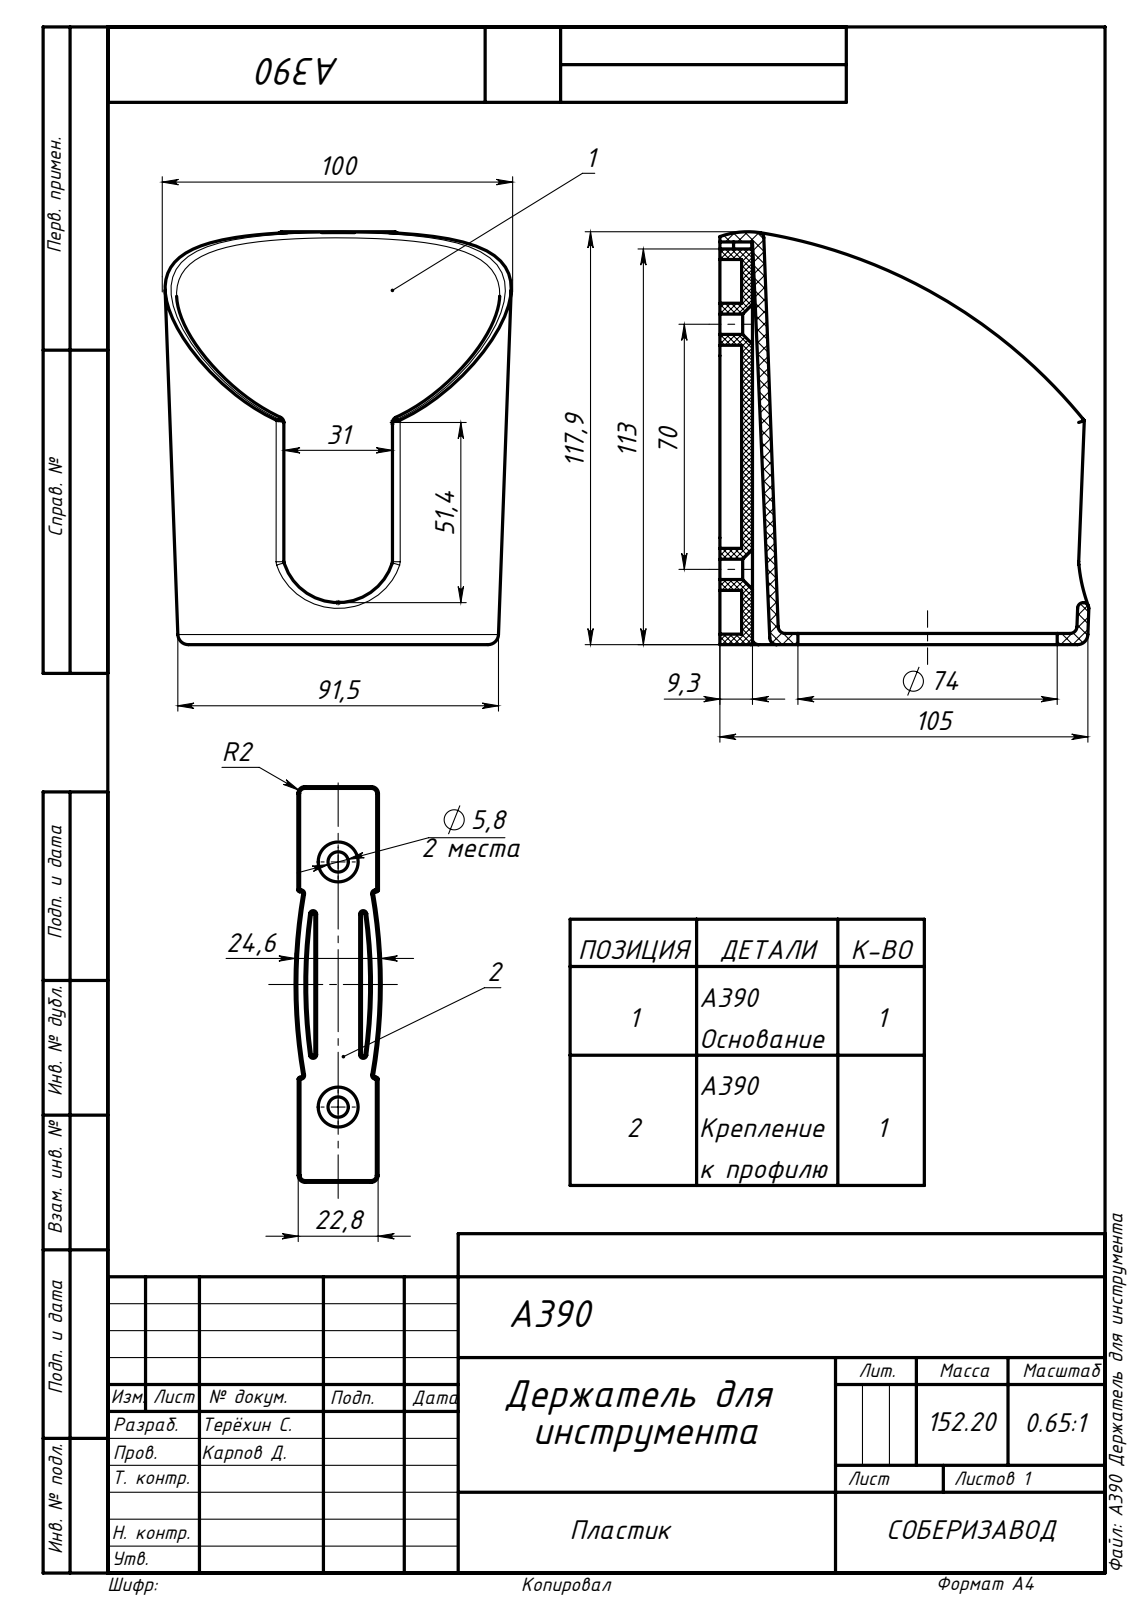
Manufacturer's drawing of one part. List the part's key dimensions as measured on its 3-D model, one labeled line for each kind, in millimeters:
Part name (STEP PRODUCT): A390 Держатель для инструмента; A390 Основание_00; A390 Крепление к профилю_00
STEP written by: SolidWorks 2020 (AUTOMOTIVE_DESIGN)
Units: millimetres
Bodies: 2 solids, 195 faces (56 planar, 82 cylindrical, 57 other)
Overall size (bounding box): 117.92 × 105.3 × 98.79
Volume: 117 829 mm³ · Surface area: 73 682 mm²
Round holes (diameter × count): ⌀5.8 ×2, ⌀74 ×1
Partial cylindrical surfaces — rounded edges, fillets, slot ends (radius × count): R0.5 ×38, R2 ×15, R3.5 ×4, R6 ×2, R150.51 ×2, R153.81 ×2, R23.67 ×1, R150 ×1
Main face-to-face distances: 9.3, 3, 3.4, 20.9, 17.5, 1.7, 12, 3.2, 5.5, 18.8
Hole centre spacings: 70
